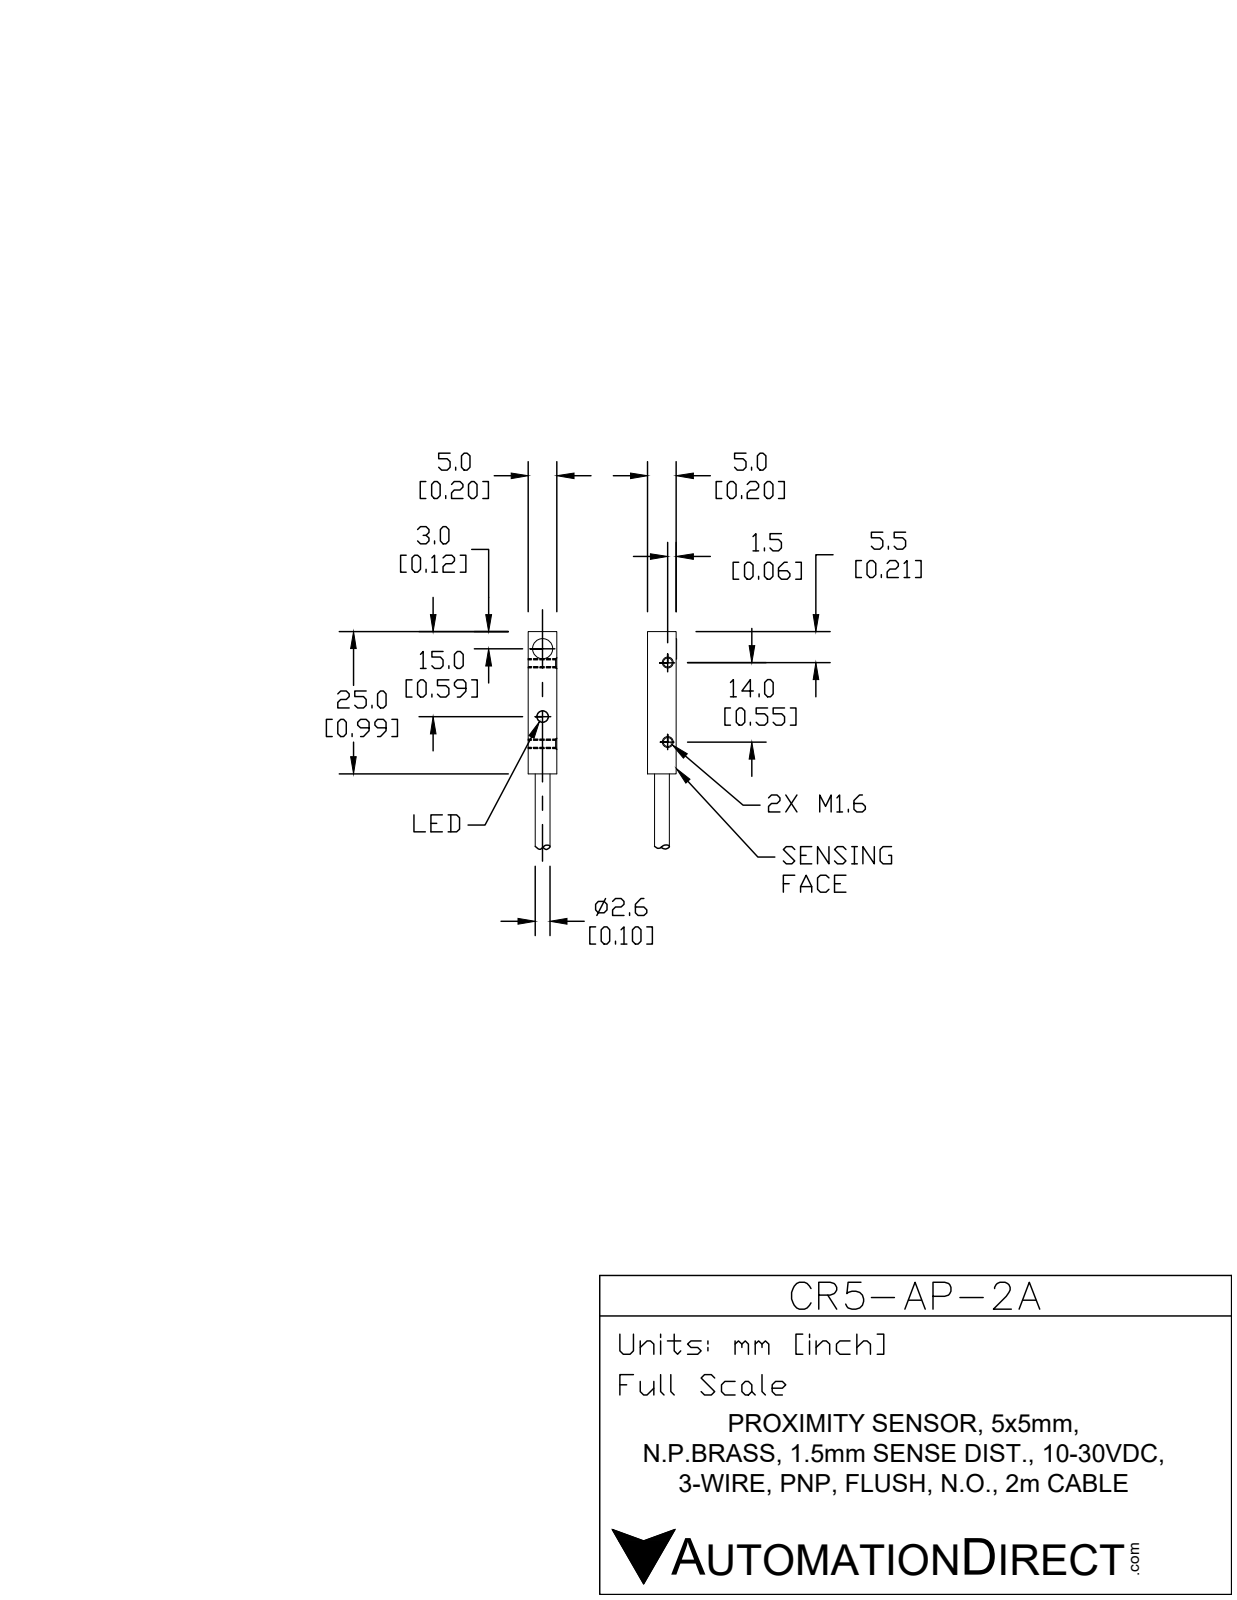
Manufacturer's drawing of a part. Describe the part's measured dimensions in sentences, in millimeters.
The part is named "CR5-AP-2A". Its 3-D file was written by "SolidWorks 2017 (AUTOMOTIVE_DESIGN)". It is 1 solid with 18 faces: 8 planar, 5 cylindrical and 5 other. Overall it measures 45 by 5 by 5 millimeters. Its volume is 720 cubic millimeters and its surface area 750 square millimeters. Round holes: 2 of diameter 1.2, 1 of diameter 1, 1 of diameter 2.6. Round bosses or shafts: 1 of diameter 2.6. The main face-to-face distances are 5, 25, 4.7, 20, 45. The hole center spacings are 12, 14.
